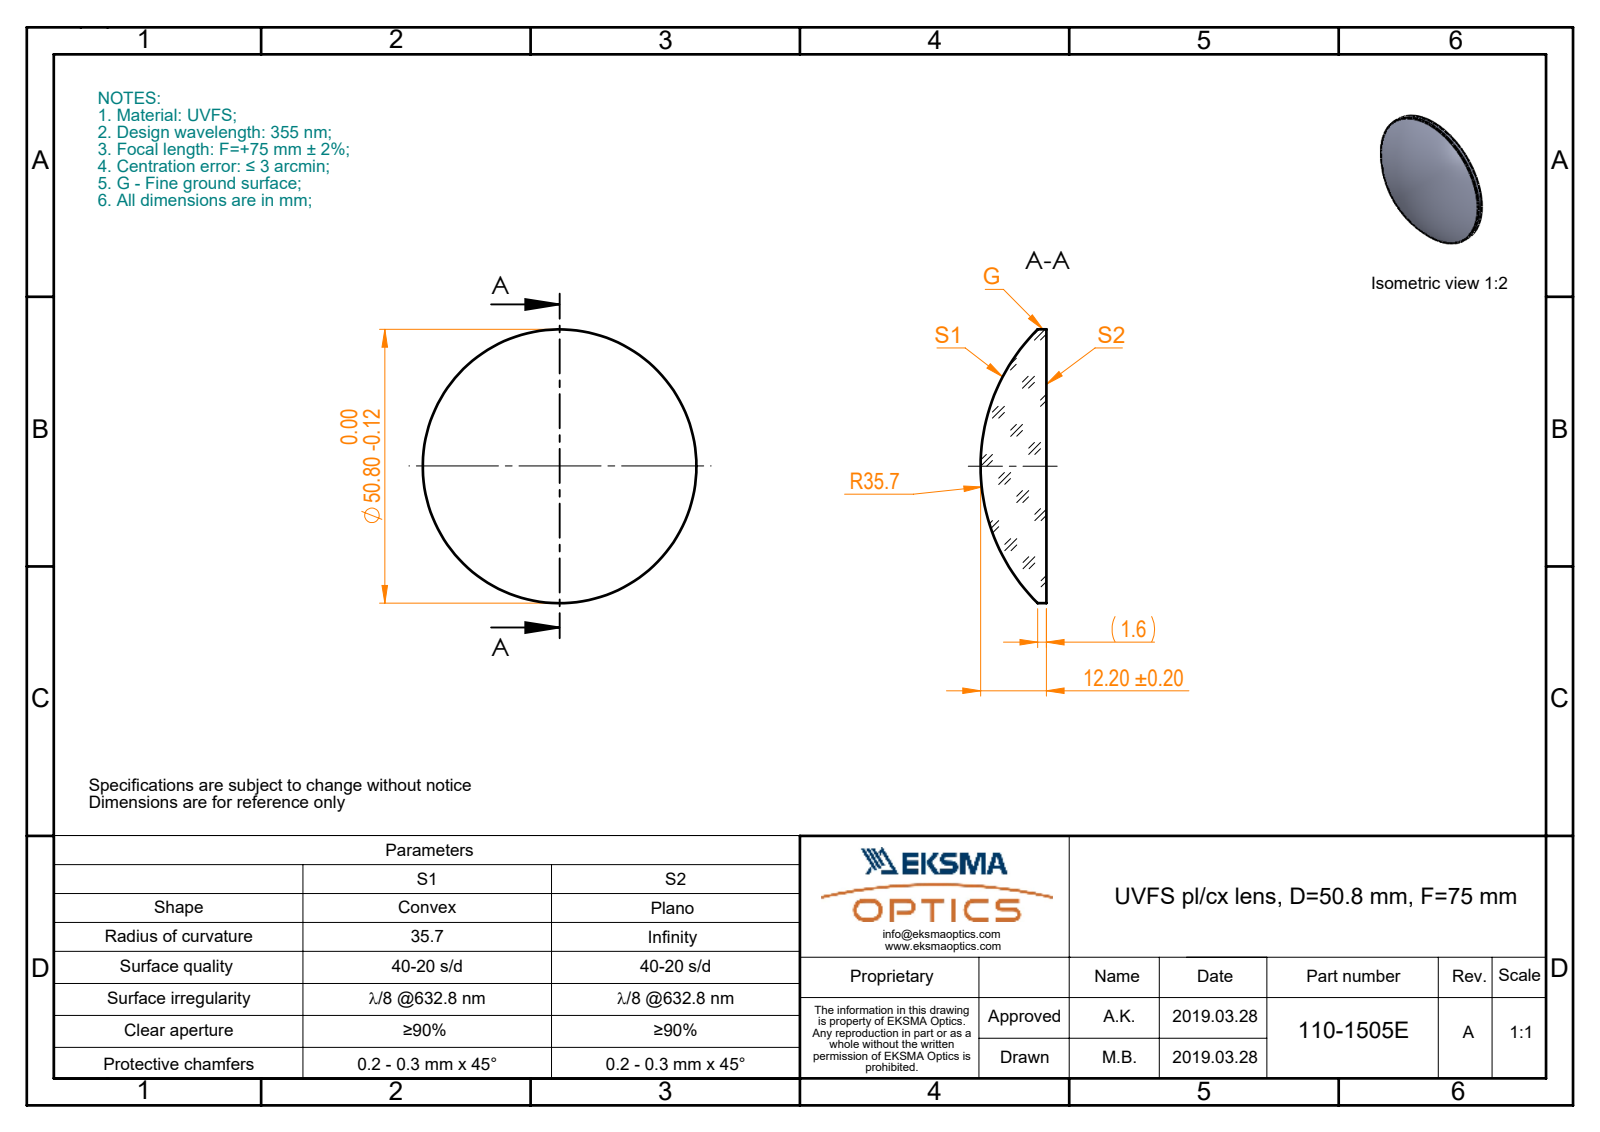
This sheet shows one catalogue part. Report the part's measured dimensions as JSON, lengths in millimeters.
{"part_name": "110-1505E UVFS pl-cx 50.8 F75", "step_written_by": "SolidWorks 2017 (CONFIG_CONTROL_DESIGN)", "units": "millimeters", "bodies": {"solids": 1, "faces": 5, "planar": 1, "cylindrical": 2, "other": 2}, "overall_size": [50.8, 50.8, 12.2], "volume_mm3": 14601, "surface_area_mm2": 4661, "round_bosses_or_shafts": [[50.8, 1]]}
